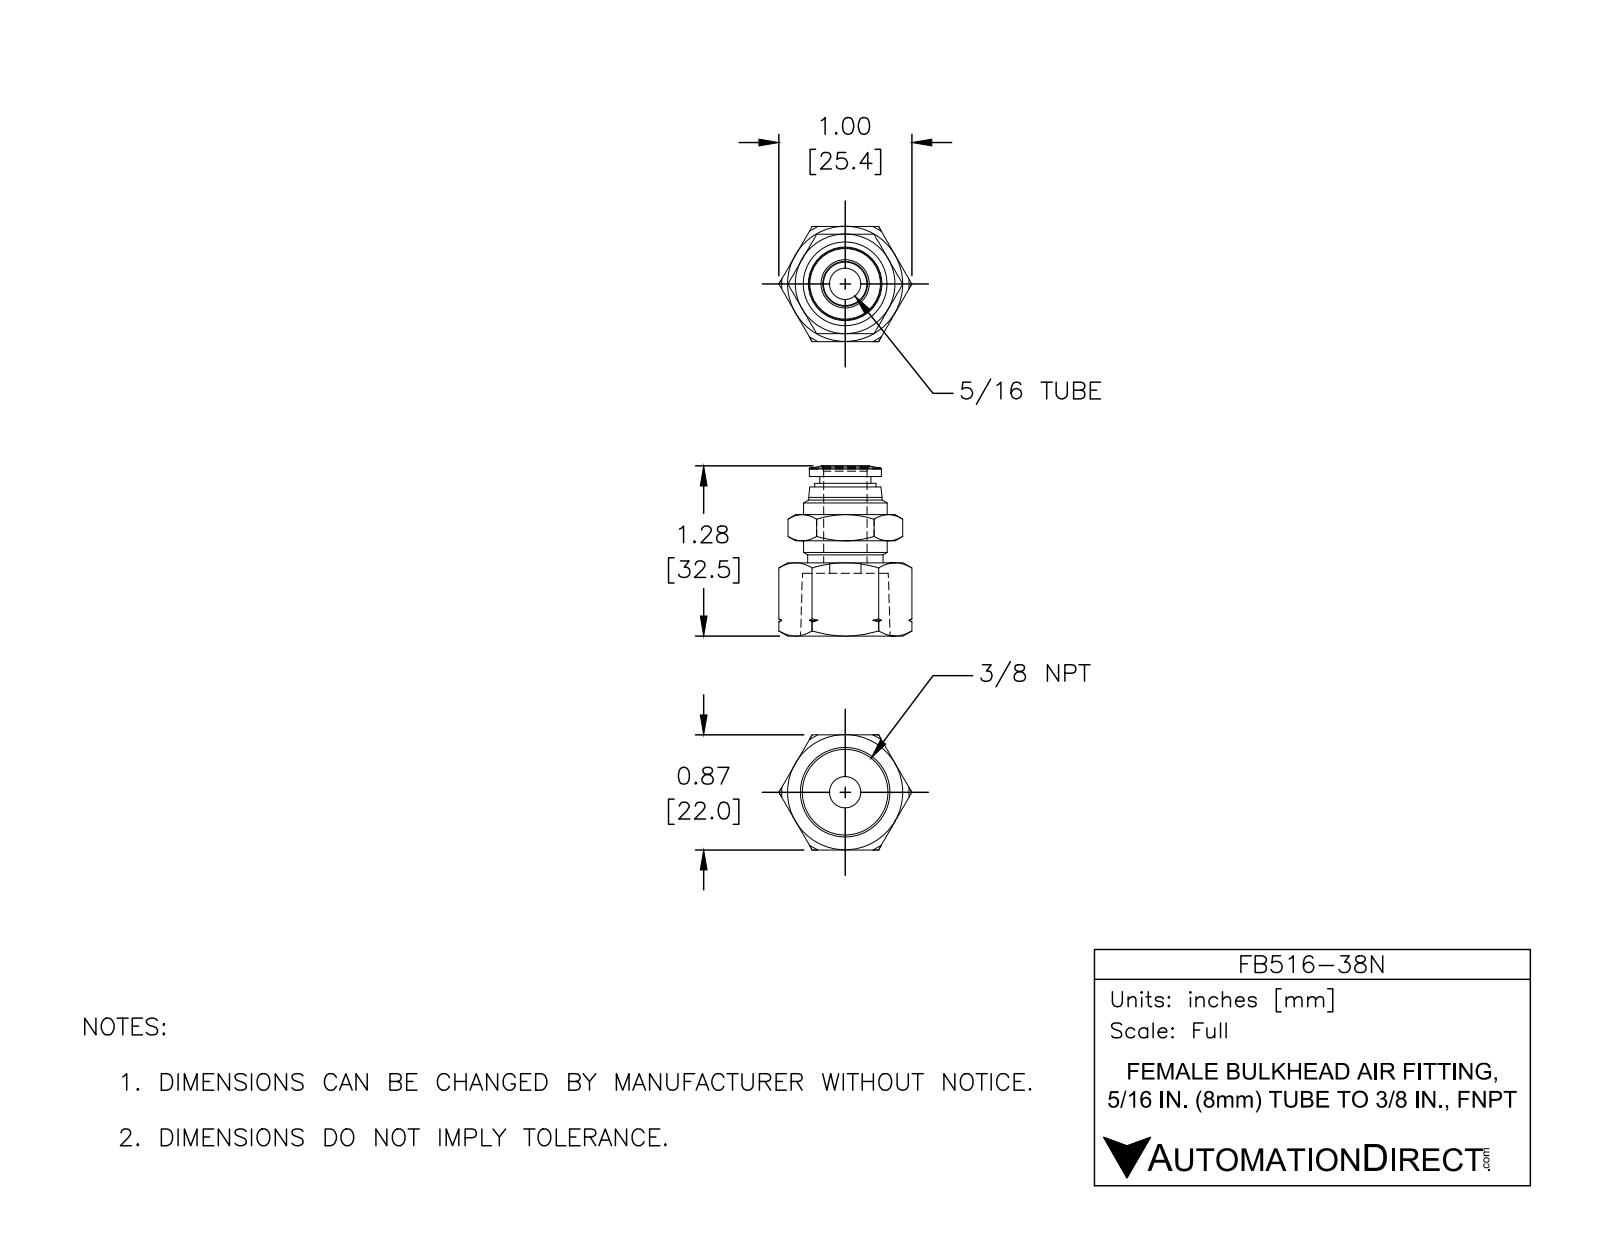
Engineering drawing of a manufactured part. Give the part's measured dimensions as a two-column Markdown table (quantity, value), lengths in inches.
| quantity | value |
| --- | --- |
| part name | FB516-38N |
| STEP written by | SolidWorks 2015 (CONFIG_CONTROL_DESIGN) |
| units | inches |
| bodies | 1 solid, 91 faces (21 planar, 18 cylindrical, 52 other) |
| overall size | 1.28 × 1 × 0.866 |
| volume | 0.356 in³ |
| surface area | 6.55 in² |
| round holes (diameter × count) | 0.236 × 1, 0.327 × 1 |
| round bosses / shafts (diameter × count) | 0.63 × 1, 0.567 × 1, 0.551 × 1, 0.543 × 1, 0.461 × 1, 0.386 × 1 |
| main face-to-face distances | 0.866, 0.059, 0.807, 0.079, 0.472, 0.551, 0.748, 0.65, 0.913, 0.441 |
